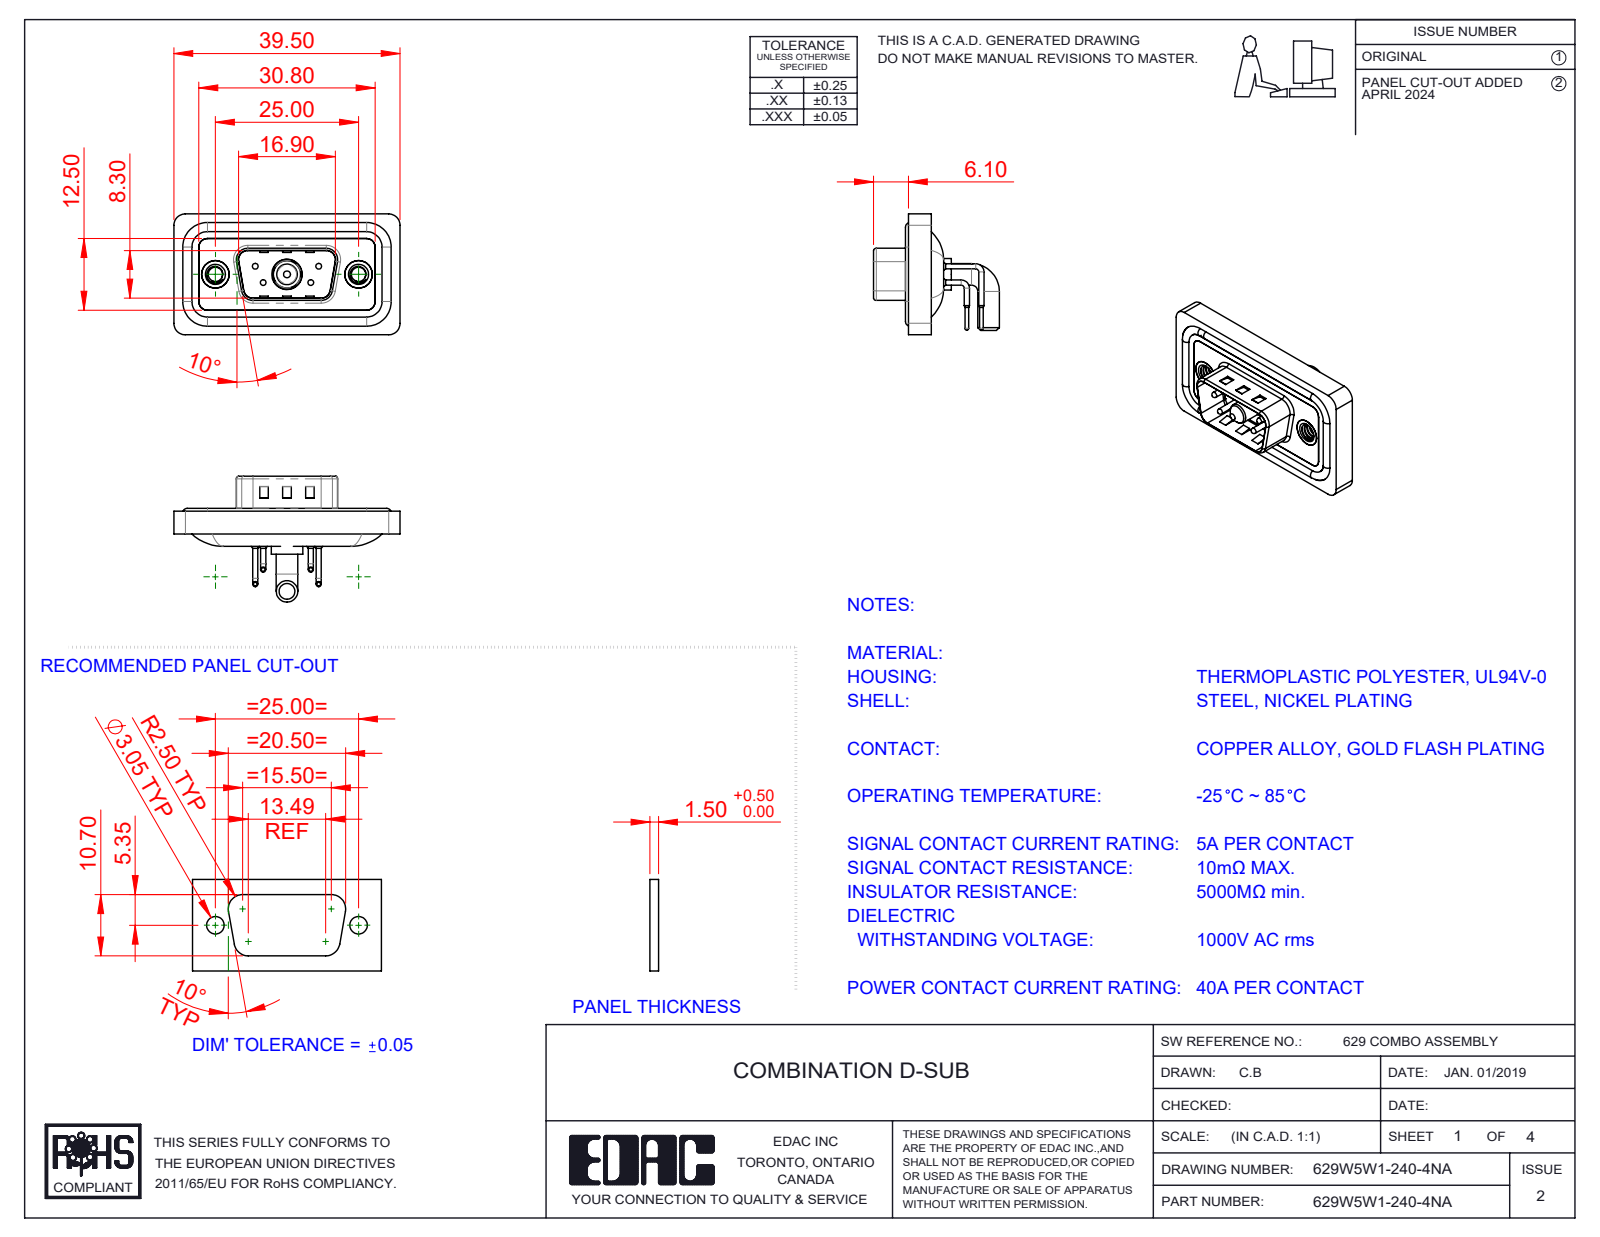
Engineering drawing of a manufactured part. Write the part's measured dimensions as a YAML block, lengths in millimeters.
part_name: "629W5W1-240-4NA; 629Combo Contact Row 2; 629Combo Shell Rear_09 Contacts; 629Combo Threaded Rivet_A (+5 more)"
step_written_by: "SolidWorks 2023 (CONFIG_CONTROL_DESIGN)"
units: millimeters
bodies: {solids: 13, faces: 888, planar: 411, cylindrical: 343, other: 134}
overall_size: [39.5, 21.98, 21.1]
volume: 4552
surface_area: 7211
round_holes:
  - {diameter: 0.75, count: 4}
  - {diameter: 1.6, count: 4}
  - {diameter: 2, count: 4}
  - {diameter: 2.5, count: 2}
  - {diameter: 4, count: 2}
  - {diameter: 4.8, count: 2}
  - {diameter: 5, count: 2}
  - {diameter: 4.85, count: 1}
  - {diameter: 5.3, count: 1}
round_bosses_or_shafts:
  - {diameter: 0.9, count: 8}
  - {diameter: 1.6, count: 4}
  - {diameter: 1.5, count: 4}
  - {diameter: 1, count: 4}
  - {diameter: 0.65, count: 4}
  - {diameter: 4.9, count: 2}
  - {diameter: 3.75, count: 2}
  - {diameter: 5.5, count: 1}
partial_cylinders:
  - {radius: 1.5, count: 18}
  - {radius: 2, count: 18}
  - {radius: 0.5, count: 8}
  - {radius: 1.6, count: 8}
  - {radius: 0.25, count: 4}
  - {radius: 0.6, count: 4}
  - {radius: 0.65, count: 4}
  - {radius: 0.9, count: 4}
face_to_face_distances: [0.4, 2.9, 1.1, 0.8, 2.1, 2.5, 1.6, 3.1, 4.5, 1.5]
hole_center_spacings: [3.16, 5.72, 7.1, 12.5, 18.1, 4.39, 4.4, 8.31]
